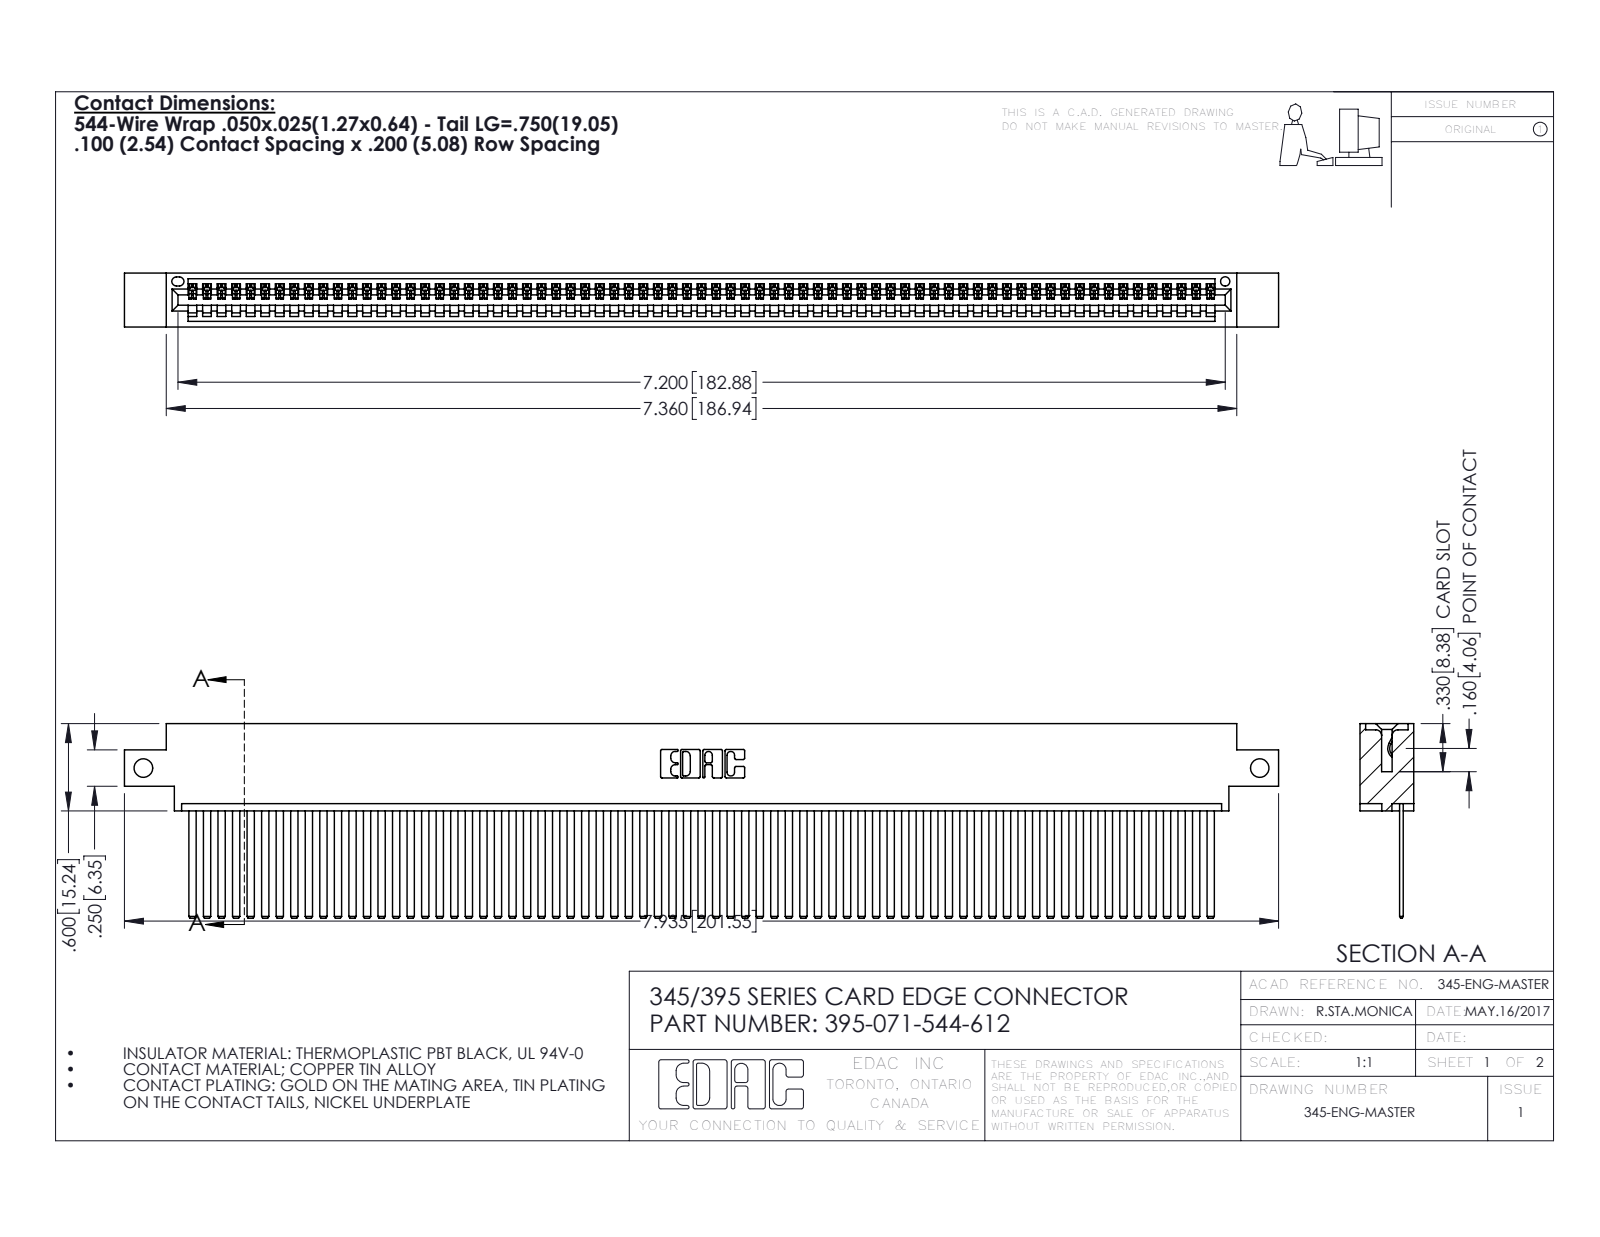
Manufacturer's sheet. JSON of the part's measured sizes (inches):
{"part_name": "345 Part_0.170 Offset - Side Mount; 395-071-544-612; 345-292-001_345-293-144", "step_written_by": "SolidWorks 2016 (CONFIG_CONTROL_DESIGN)", "units": "inches", "bodies": {"solids": 72, "faces": 3822, "planar": 2640, "cylindrical": 1182, "other": 0}, "overall_size": [7.935, 1.337, 0.37], "volume_in3": 1.221, "surface_area_in2": 45.61, "round_holes": [[0.128, 2], [0.064, 1]], "partial_cylinders_radius": [[0.006, 142], [0.01, 22], [0.007, 6], [0.031, 6], [0.026, 3], [0.031, 2], [0.04, 2], [0.014, 1]], "face_to_face_distances": [0.072, 0.298, 0.025, 0.098, 0.272, 0.37, 0.2, 0.225, 0.175, 0.149], "hole_center_spacings": [7.675]}
